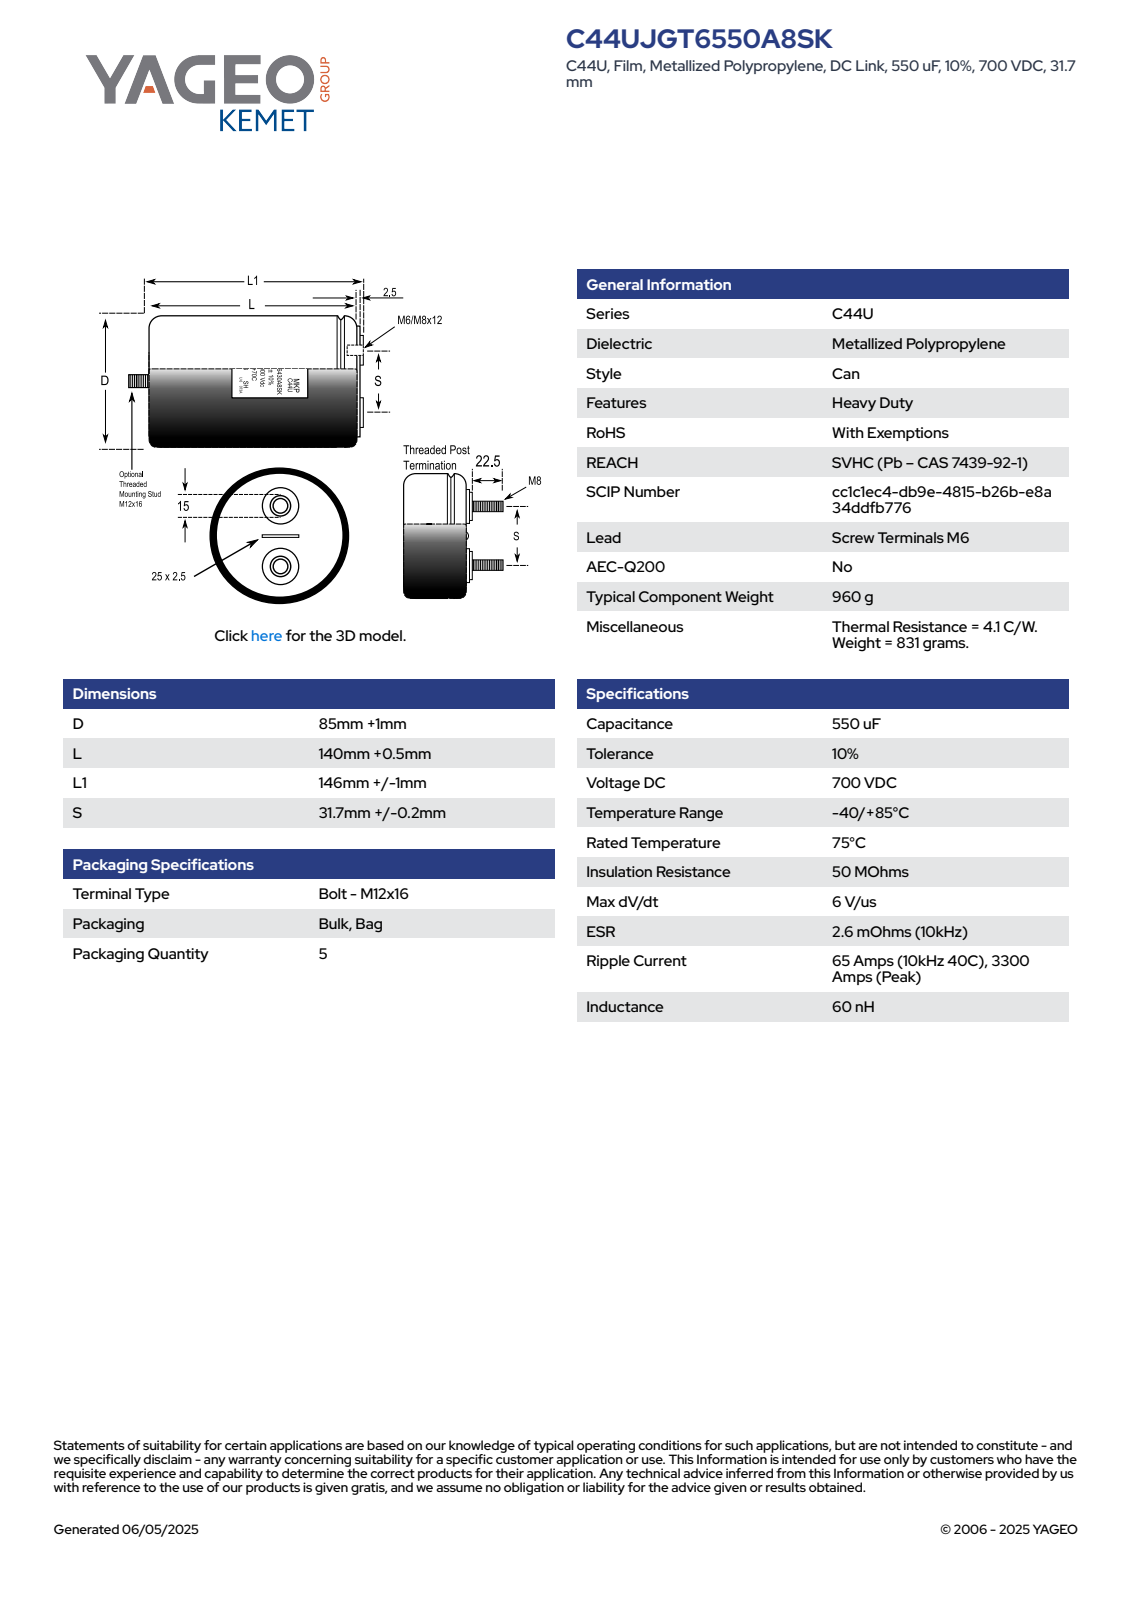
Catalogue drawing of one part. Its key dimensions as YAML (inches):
part_name: "CFP_C44U_T_85X140_D86L140.5S31.9"
step_written_by: "SolidWorks 2021 (AUTOMOTIVE_DESIGN)"
units: inches
bodies: {solids: 1, faces: 104, planar: 36, cylindrical: 29, other: 39}
overall_size: [6.26, 3.386, 3.386]
volume: 49.46
surface_area: 76.44
round_holes:
  - {diameter: 0.236, count: 2}
round_bosses_or_shafts:
  - {diameter: 0.709, count: 2}
  - {diameter: 0.591, count: 2}
  - {diameter: 3.386, count: 1}
  - {diameter: 2.756, count: 1}
  - {diameter: 0.472, count: 1}
partial_cylinders:
  - {radius: 1.693, count: 1}
face_to_face_distances: [5.532, 5.63, 0.098, 5.581, 0.049, 0.049, 0.63, 6.162, 6.211, 6.26]
hole_center_spacings: [1.256]
